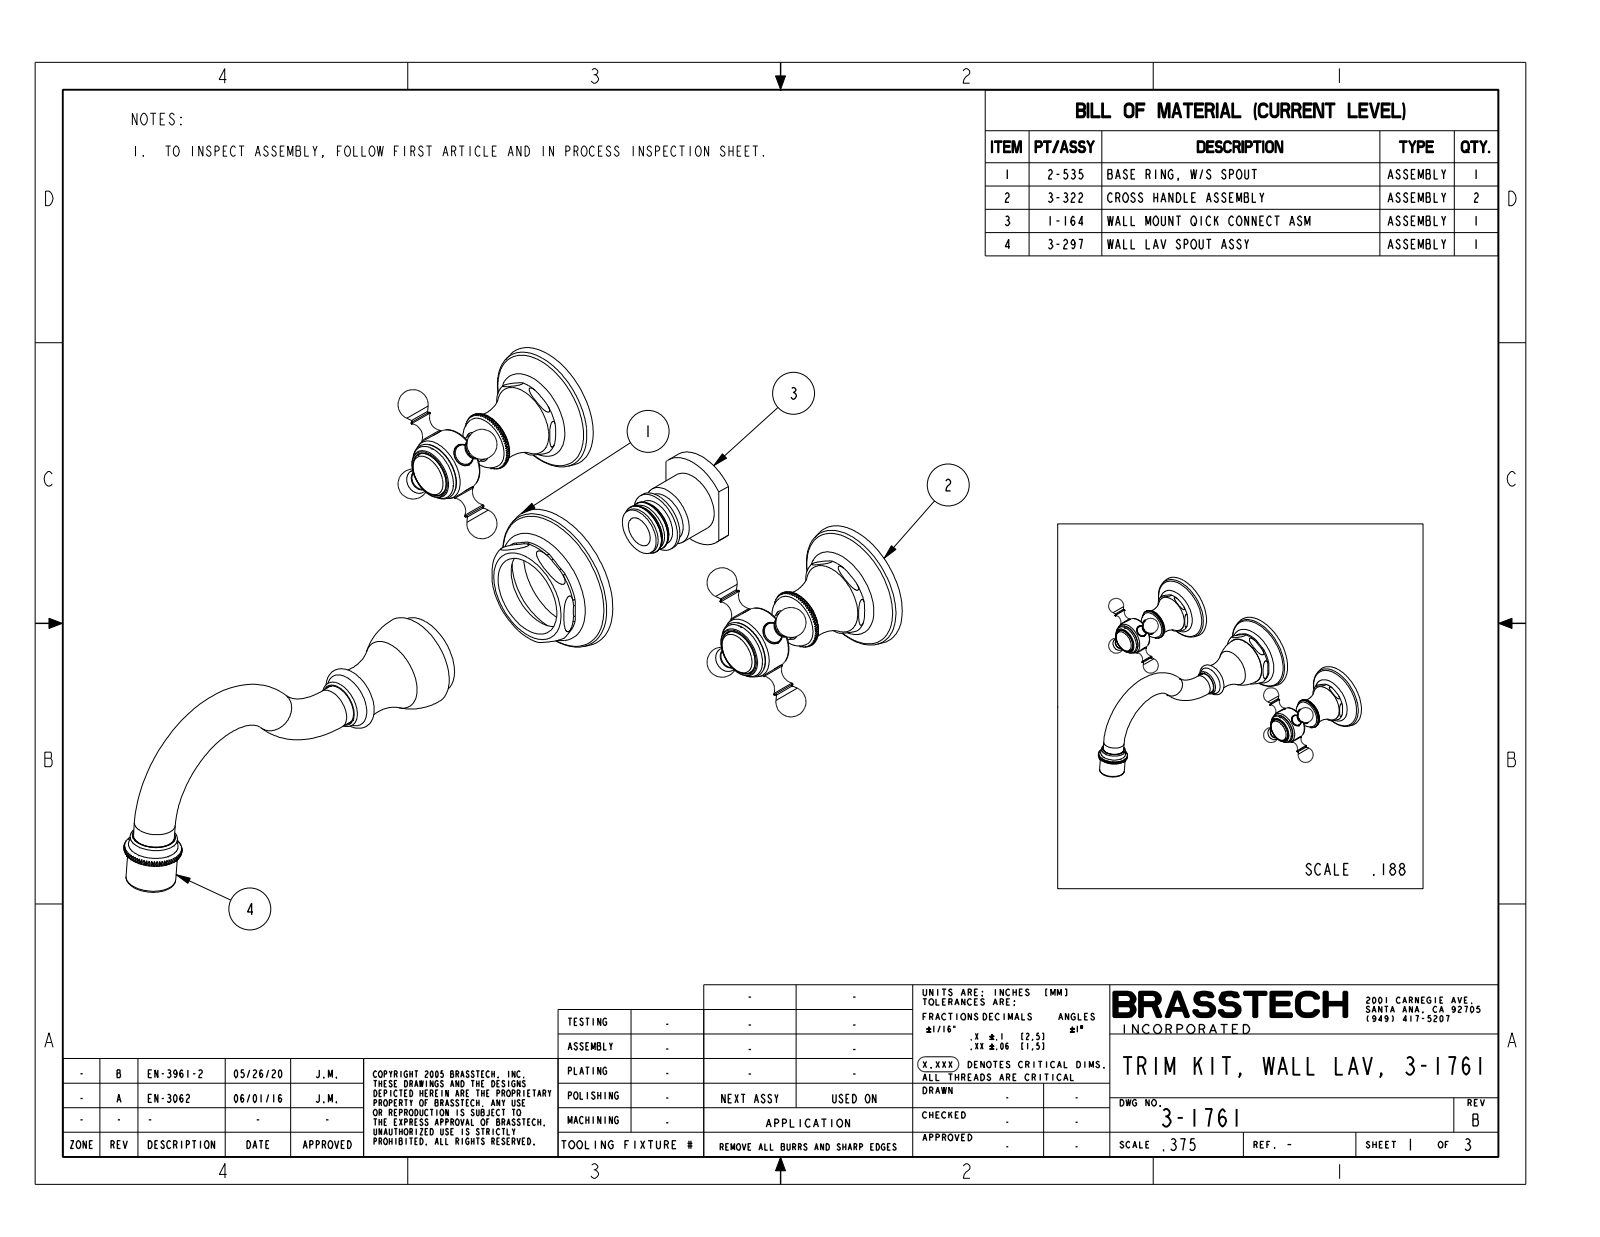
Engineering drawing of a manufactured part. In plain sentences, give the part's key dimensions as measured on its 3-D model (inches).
The part is named "3-1761_SW0002". Its 3-D file was written by "CREO PARAMETRIC BY PTC INC, 2018400 (AUTOMOTIVE_DESIGN)". It is 3 solids with 745 faces: 467 planar, 50 cylindrical and 228 other. Overall it measures 10.365 by 8.178 by 3.215 inches. Its volume is 17.3 cubic inches and its surface area 90.69 square inches. Round holes: 8 of diameter 0.41, 2 of diameter 0.855. Round bosses or shafts: 8 of diameter 0.392, 2 of diameter 0.84, 2 of diameter 0.75, 2 of diameter 0.5, 1 of diameter 0.91. The main face-to-face distances are 2.29, 1.86, 1.375, 0.383, 2.243, 1.757, 3.617, 4, 3, 0.71. The hole center spacings are 5.657, 8.
